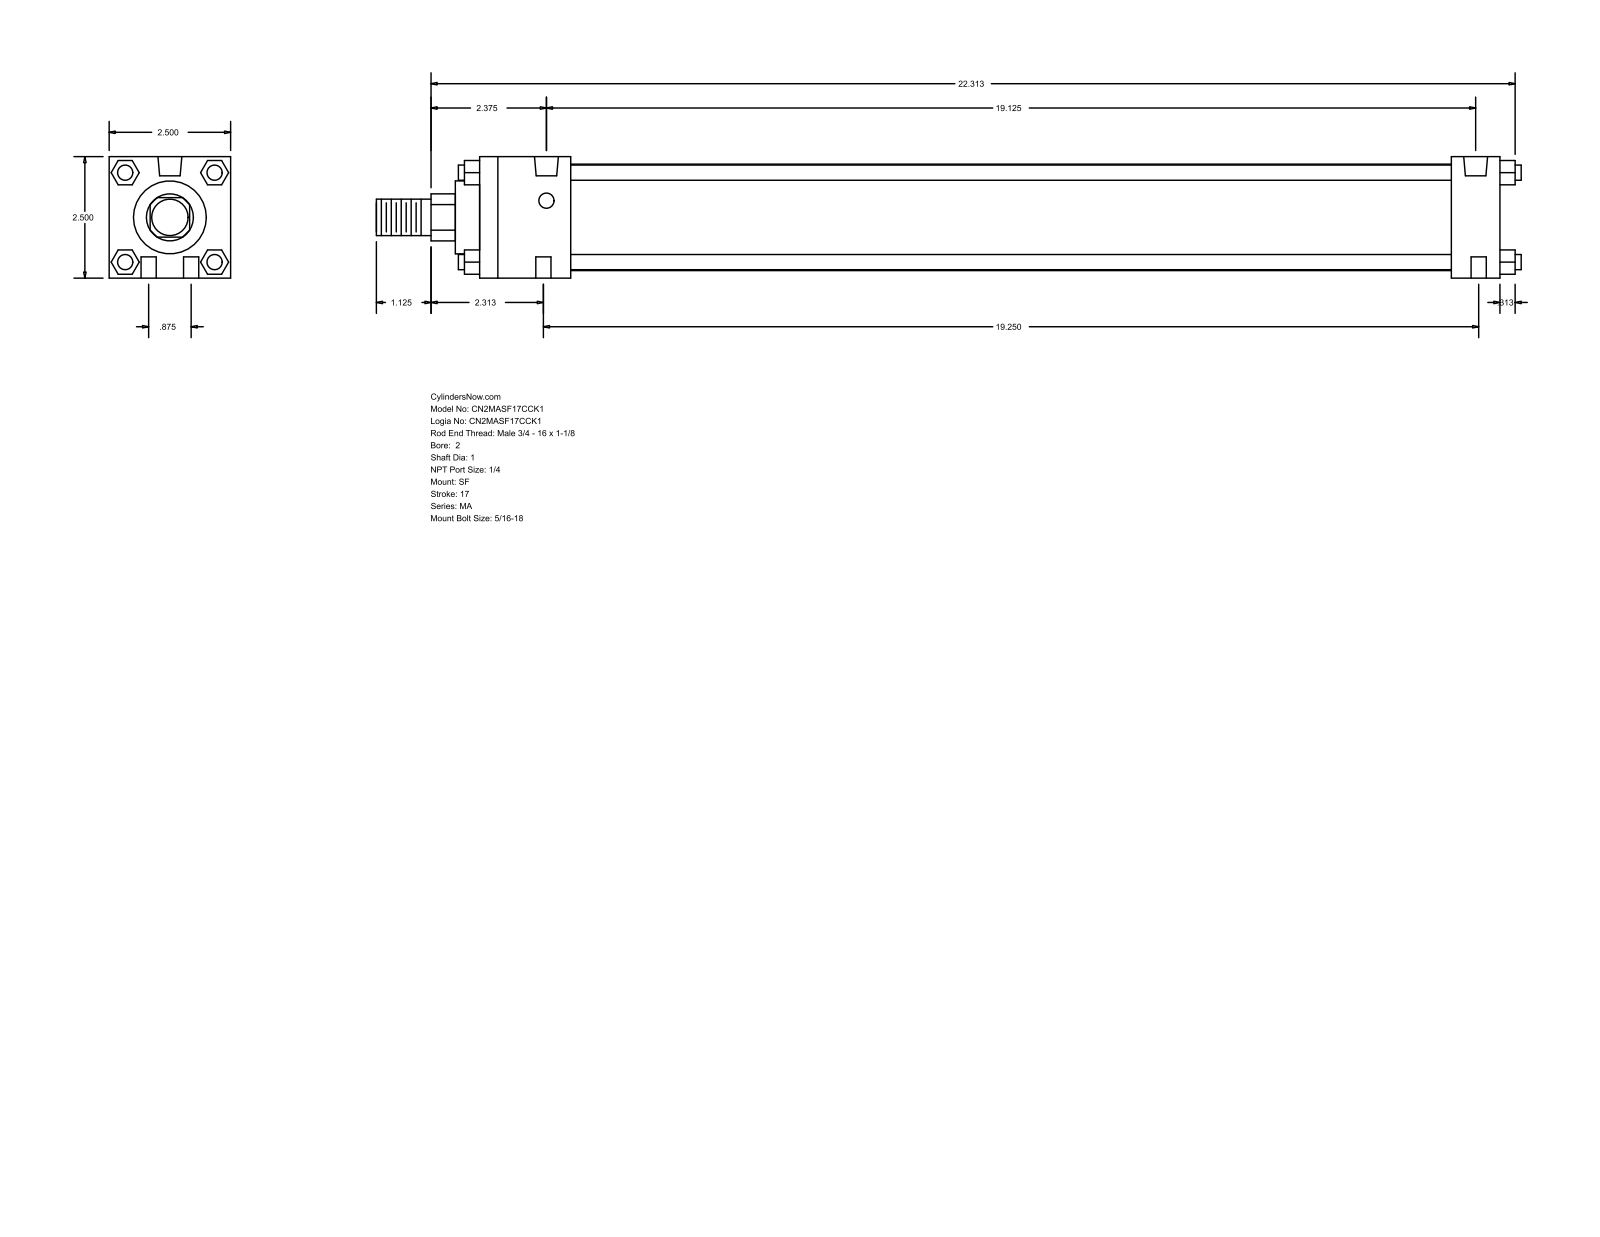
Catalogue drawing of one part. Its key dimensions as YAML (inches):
part_name: "MA_SF__0200_1"
step_written_by: "GSSL Pune (CONFIG_CONTROL_DESIGN)"
units: inches
bodies: {solids: 0, faces: 124, planar: 94, cylindrical: 30, other: 0}
overall_size: [23.563, 2.5, 2.5]
round_holes:
  - {diameter: 0.313, count: 6}
  - {diameter: 0.492, count: 2}
round_bosses_or_shafts:
  - {diameter: 0.313, count: 4}
  - {diameter: 2.19, count: 1}
  - {diameter: 1.5, count: 1}
  - {diameter: 1, count: 1}
  - {diameter: 0.75, count: 1}
partial_cylinders:
  - {radius: 0.484, count: 1}
face_to_face_distances: [2.5, 21, 0.5, 1, 20, 1.875, 18.125, 19.125, 1.593, 0.92]
hole_center_spacings: [0.442, 19.193, 0.875, 19.125, 19.25, 19.27]
